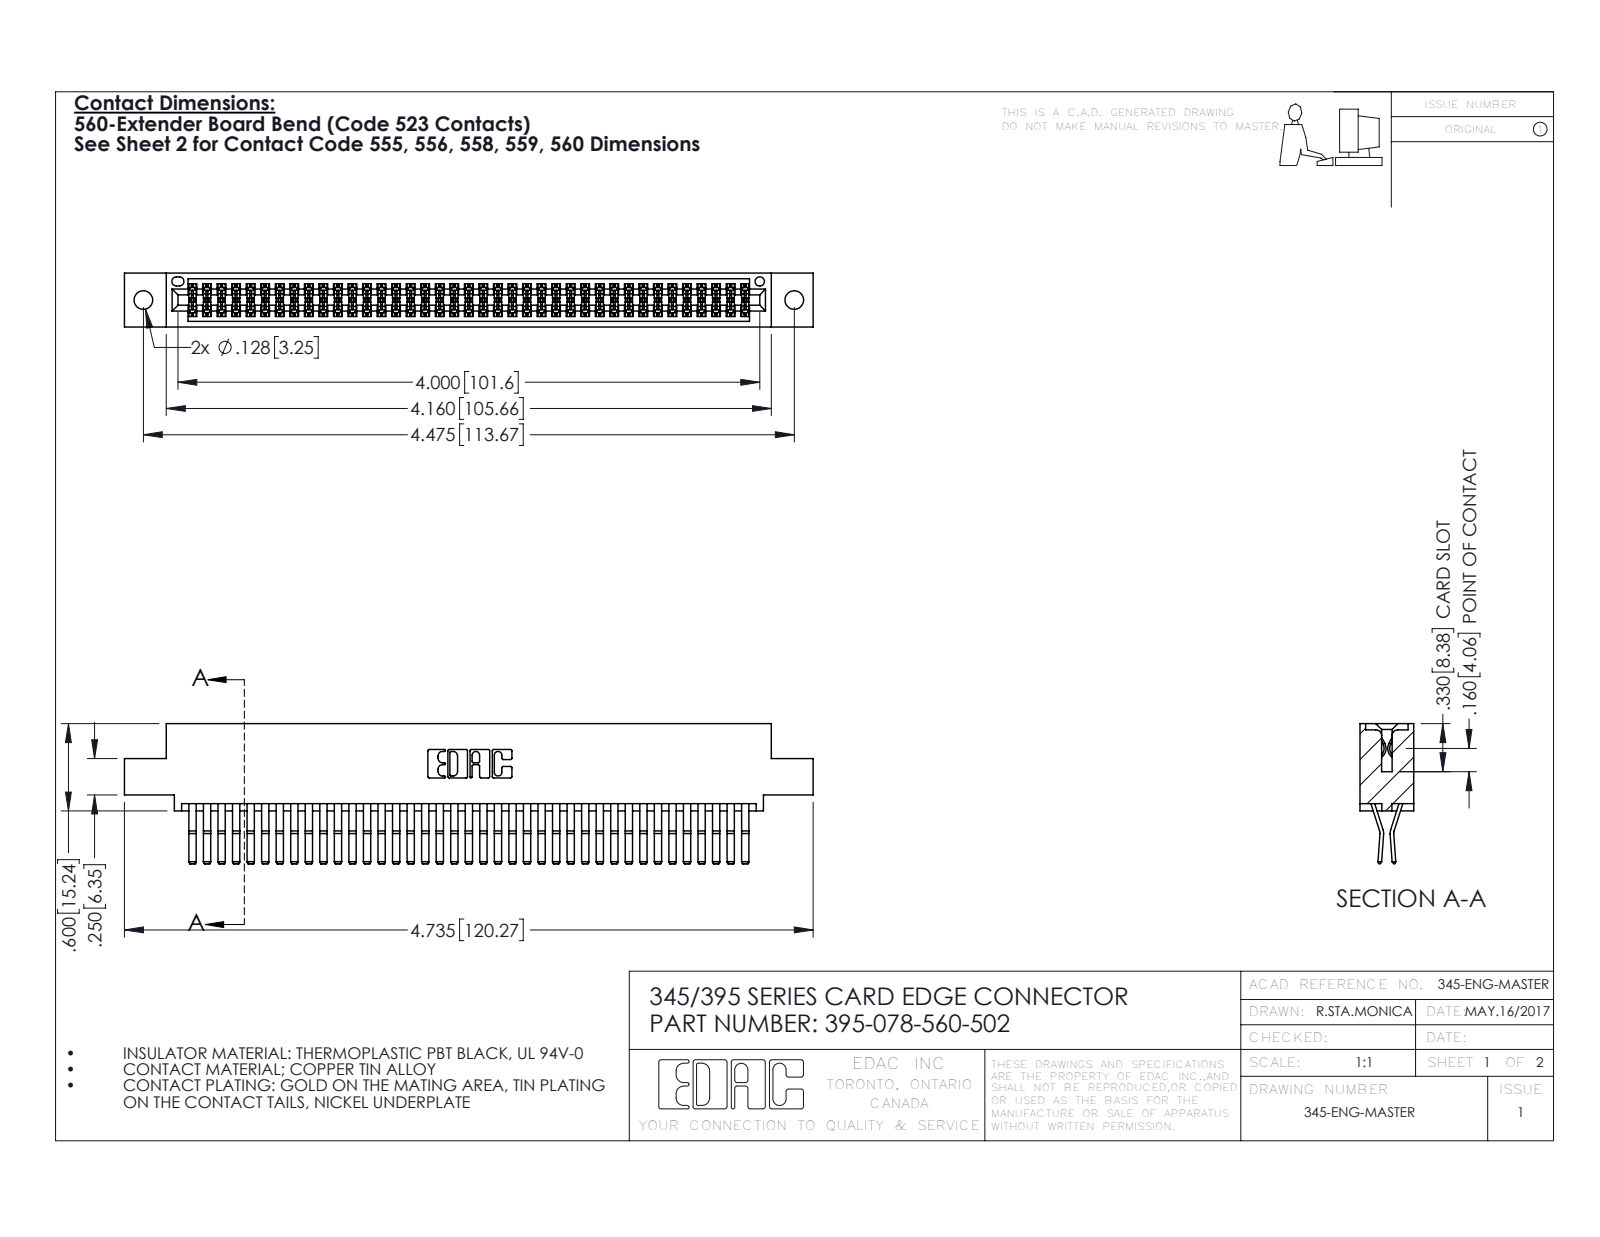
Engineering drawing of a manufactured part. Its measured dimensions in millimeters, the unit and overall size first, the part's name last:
Units: millimetres
Overall size (bounding box): 120.3 × 24.4 × 9.4
Round holes (diameter × count): ⌀3.3 ×2, ⌀1.6 ×1
Partial cylindrical surfaces — rounded edges, fillets, slot ends (radius × count): R0.2 ×117, R0.3 ×22, R0.2 ×6, R0.8 ×6, R0.7 ×3, R0.3 ×2, R0.4 ×2, R0.5 ×2
Main face-to-face distances: 0.6, 7.6, 1.8, 9.4, 5.1, 2.5, 6.9, 5.7, 4.4, 3.8
Hole centre spacings: 6.9, 107.7, 113.7
Volume: 12 100 mm³ · Surface area: 18 900 mm²
Bodies: 79 solids, 4186 faces (2658 planar, 1528 cylindrical, 0 other)
Part name (STEP PRODUCT): 345 Part_0.110 Offset - 0.128 Dia; 345-292-001_560 Tail; 395-078-560-502
STEP written by: SolidWorks 2016 (CONFIG_CONTROL_DESIGN)
